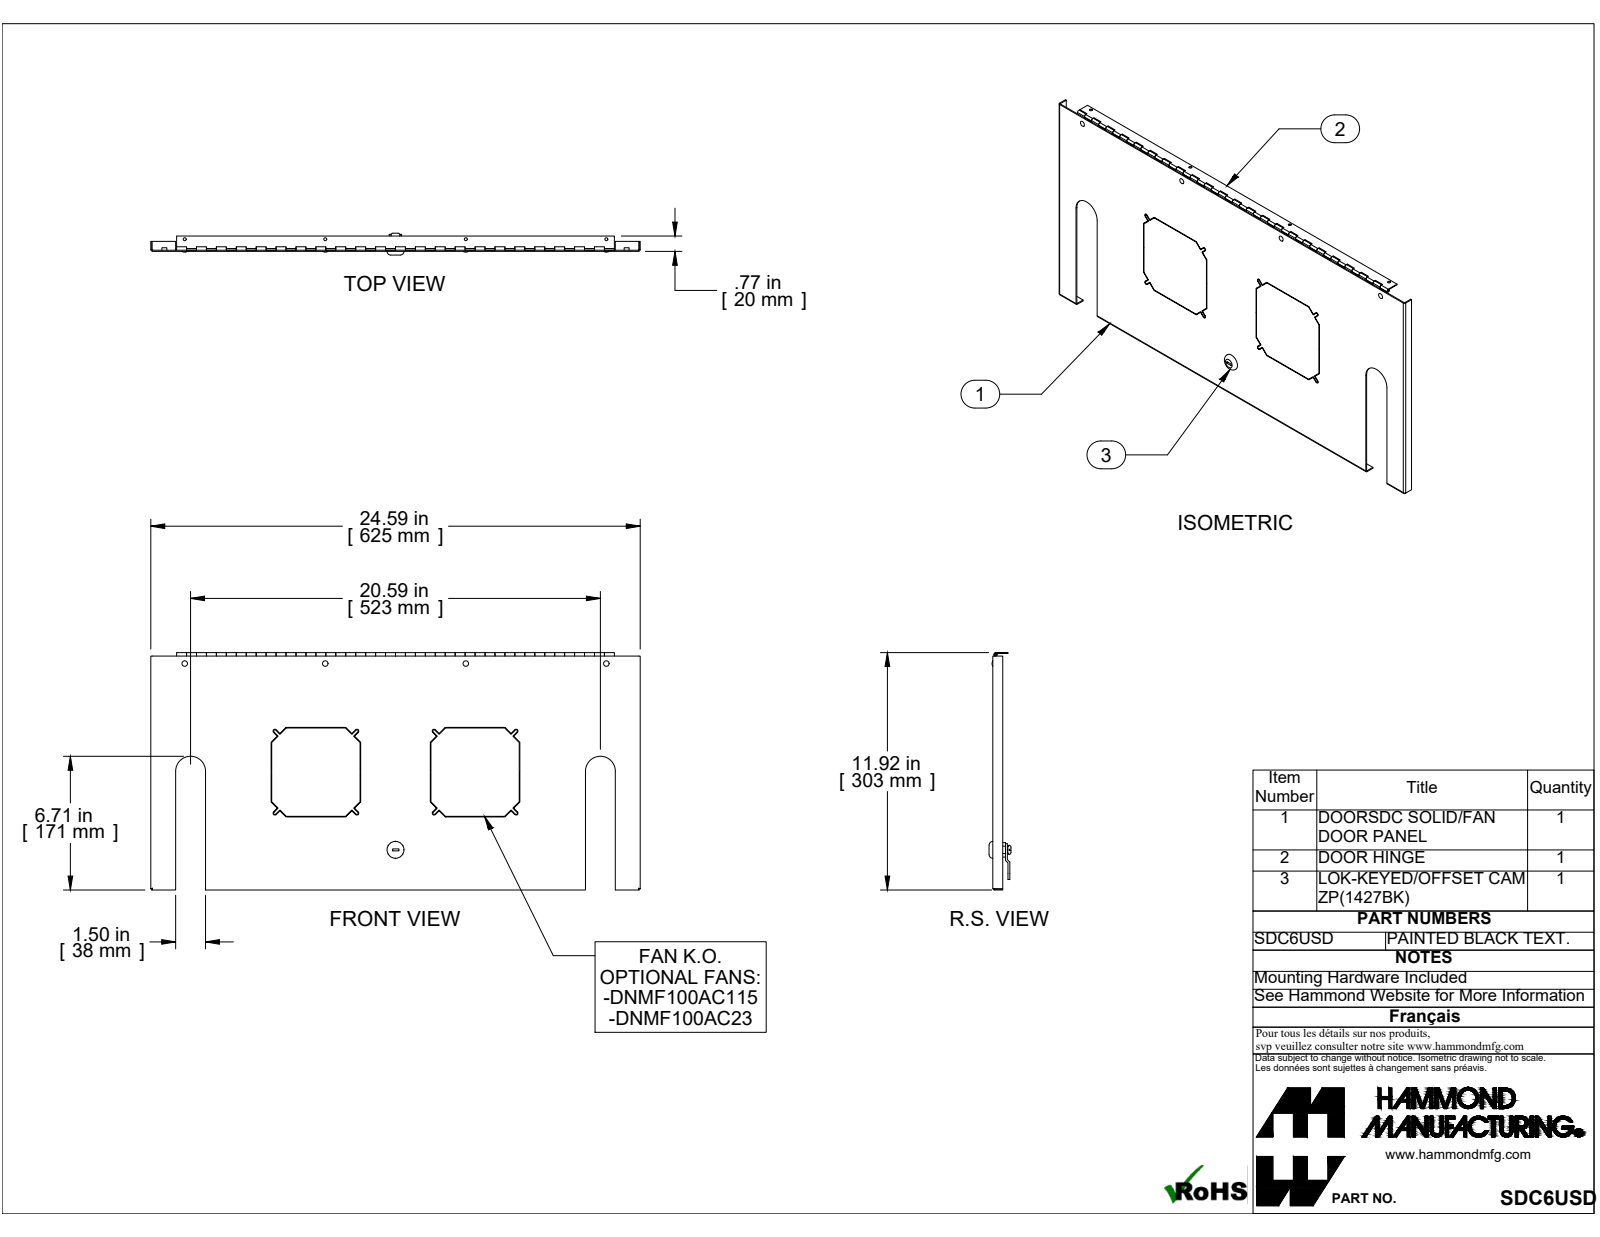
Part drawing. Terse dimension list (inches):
name: SDC6USD
written by: SolidWorks 2019 (CONFIG_CONTROL_DESIGN)
unit: in
bodies: 15 solids, 570 faces (412 planar, 142 cylindrical, 16 other)
size: 24.594 × 11.924 × 1.1
volume: 18.58 in³; area: 672.4 in²
holes: 8× ⌀0.15, 4× ⌀0.126, 1× ⌀0.092, 1× ⌀0.125, 1× ⌀0.204, 1× ⌀0.597
bosses: 1× ⌀0.728, 1× ⌀0.232, 1× ⌀0.174, 1× ⌀0.08
rounds: 8× R0.064, 8× R0.094, 3× R0.029, 3× R0.086, 2× R0.31, 2× R0.75, 1× R0.38
face distances: 0.057, 0.041, 0.057, 0.098, 24.537, 11.826, 11.867, 11.883, 11.924, 24.48
hole spacings: 7.063, 14.125, 7.062, 10.001, 11.451, 14.134, 15.195, 21.187
